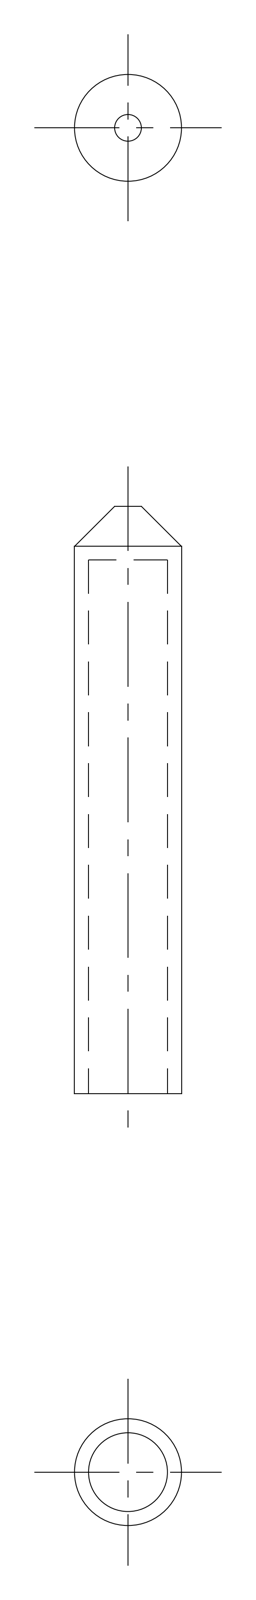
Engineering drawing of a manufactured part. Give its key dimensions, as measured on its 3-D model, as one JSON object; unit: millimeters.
{"part_name": "67109426", "step_written_by": "CADfix (AUTOMOTIVE_DESIGN)", "units": "millimeters", "bodies": {"solids": 1, "faces": 9, "planar": 0, "cylindrical": 0, "other": 9}, "overall_size": [44, 8, 8], "volume_mm3": 1036, "surface_area_mm2": 1894}
